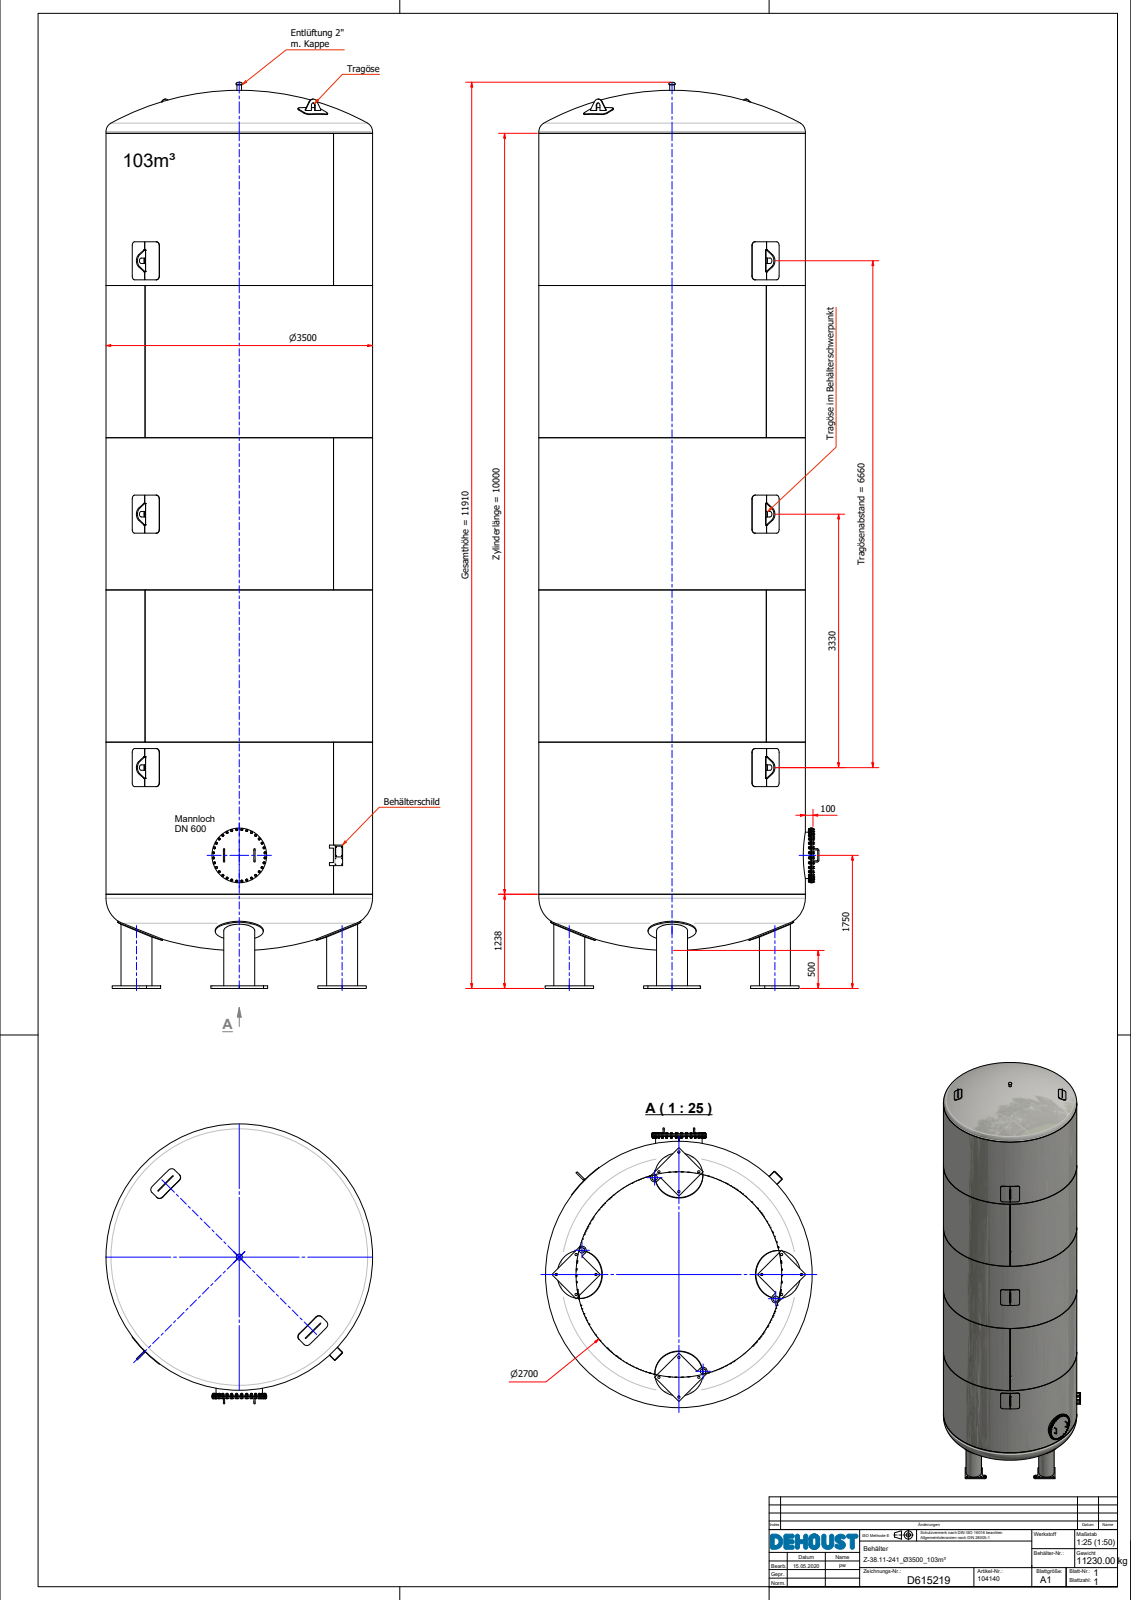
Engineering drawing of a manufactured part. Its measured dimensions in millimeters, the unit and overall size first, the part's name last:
Units: millimetres
Overall size (bounding box): 11909.62 × 3678 × 3500
Round holes (diameter × count): ⌀13.84 ×32, ⌀17 ×32, ⌀18 ×32, ⌀30 ×16, ⌀5 ×8, ⌀6.5 ×4, ⌀70 ×4, ⌀250 ×4, ⌀384.4 ×4, ⌀54.5 ×1, ⌀60.3 ×1, ⌀78.3 ×1
Round bosses / shafts (diameter × count): ⌀16 ×38, ⌀30 ×32, ⌀22.49 ×32, ⌀630 ×4, ⌀406.4 ×4, ⌀3500 ×1, ⌀720 ×1, ⌀660 ×1
Partial cylindrical surfaces — rounded edges, fillets, slot ends (radius × count): R56 ×8, R10 ×4, R55 ×4, R36 ×3, R95 ×3, R2 ×2, R7 ×2, R35 ×2
Main face-to-face distances: 35, 16, 2000, 4000, 19, 6000, 1238.32, 1203.32, 3, 8000
Hole centre spacings: 480.83, 628.23, 676.72, 66.65, 599.7, 197.39, 565.39, 260.22
Volume: 808 500 000 mm³ · Surface area: 283 500 000 mm²
Bodies: 138 solids, 1600 faces (821 planar, 353 cylindrical, 426 other)
Part name (STEP PRODUCT): D615219-0_-Behälter_Shrinkwrap_3
STEP written by: Autodesk Inventor 2019 (AUTOMOTIVE_DESIGN)
